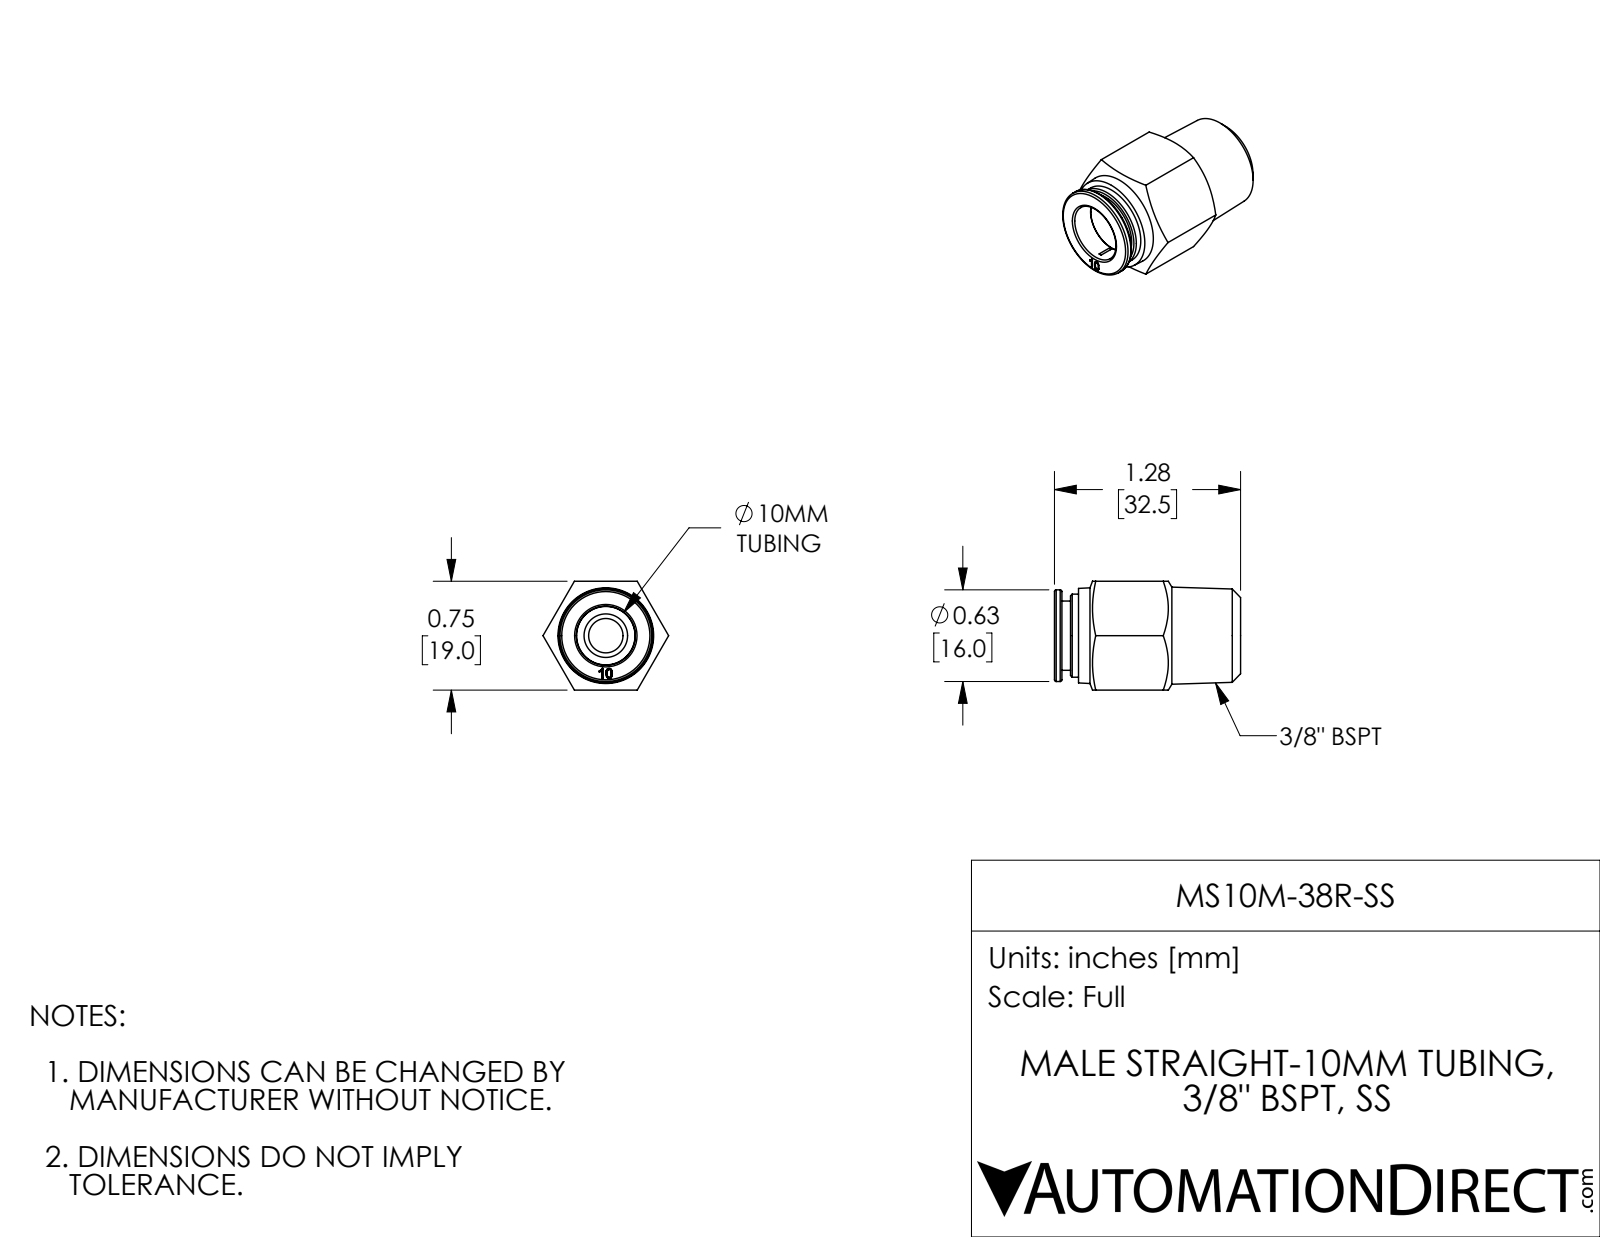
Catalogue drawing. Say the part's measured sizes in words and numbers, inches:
The part is named "MS10M-38R-SS". Its 3-D file was written by "SolidWorks 2017 (AUTOMOTIVE_DESIGN)". It is 1 solid with 78 faces: 27 planar, 12 cylindrical and 39 other. Overall it measures 1.28 by 0.864 by 0.748 inches. Its volume is 0.367 cubic inches and its surface area 5.257 square inches. Round holes: 1 of diameter 0.236, 1 of diameter 0.402, 1 of diameter 0.406. Round bosses or shafts: 1 of diameter 0.63, 1 of diameter 0.571, 1 of diameter 0.476. The main face-to-face distances are 0.748, 1.28, 1.228, 0.051, 1.114, 0.114, 0.165, 0.5, 0.614, 0.728.
